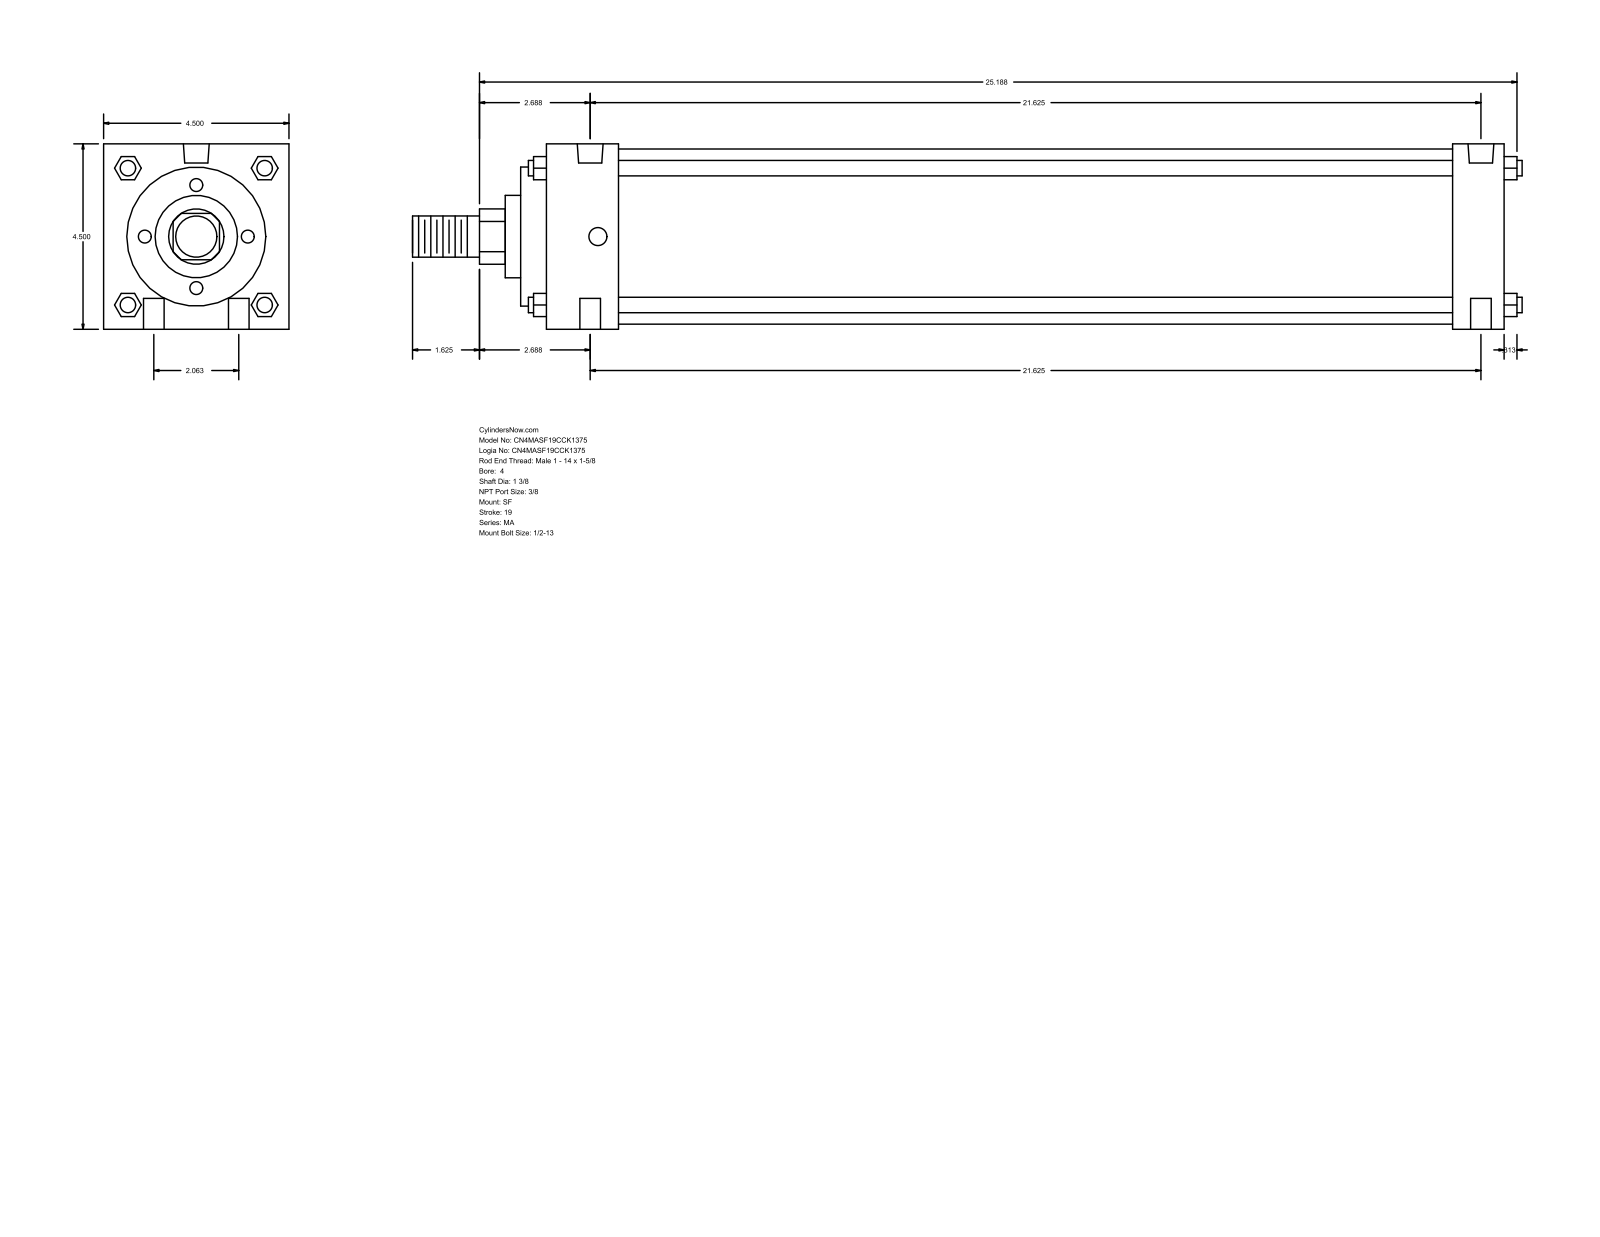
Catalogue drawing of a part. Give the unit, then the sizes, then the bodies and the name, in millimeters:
Units: millimetres
Overall size (bounding box): 684.21 × 114.3 × 114.3
Round holes (diameter × count): ⌀12.7 ×4, ⌀11.11 ×2, ⌀15.93 ×2
Round bosses / shafts (diameter × count): ⌀9.53 ×4, ⌀107.95 ×1, ⌀85.72 ×1, ⌀50.8 ×1, ⌀34.92 ×1, ⌀25.4 ×1
Partial cylindrical surfaces — rounded edges, fillets, slot ends (radius × count): R17.06 ×1
Main face-to-face distances: 114.3, 590.56, 15.87, 606.43, 574.68, 558.81, 31.75, 60.32, 44.45, 514.36
Hole centre spacings: 26.19, 549.9, 549.28, 52.38, 551.77, 539.74
Bodies: 0 solids, 126 faces (95 planar, 31 cylindrical, 0 other)
Part name (STEP PRODUCT): MA_SF__0400_1.375
STEP written by: GSSL Pune (CONFIG_CONTROL_DESIGN)
